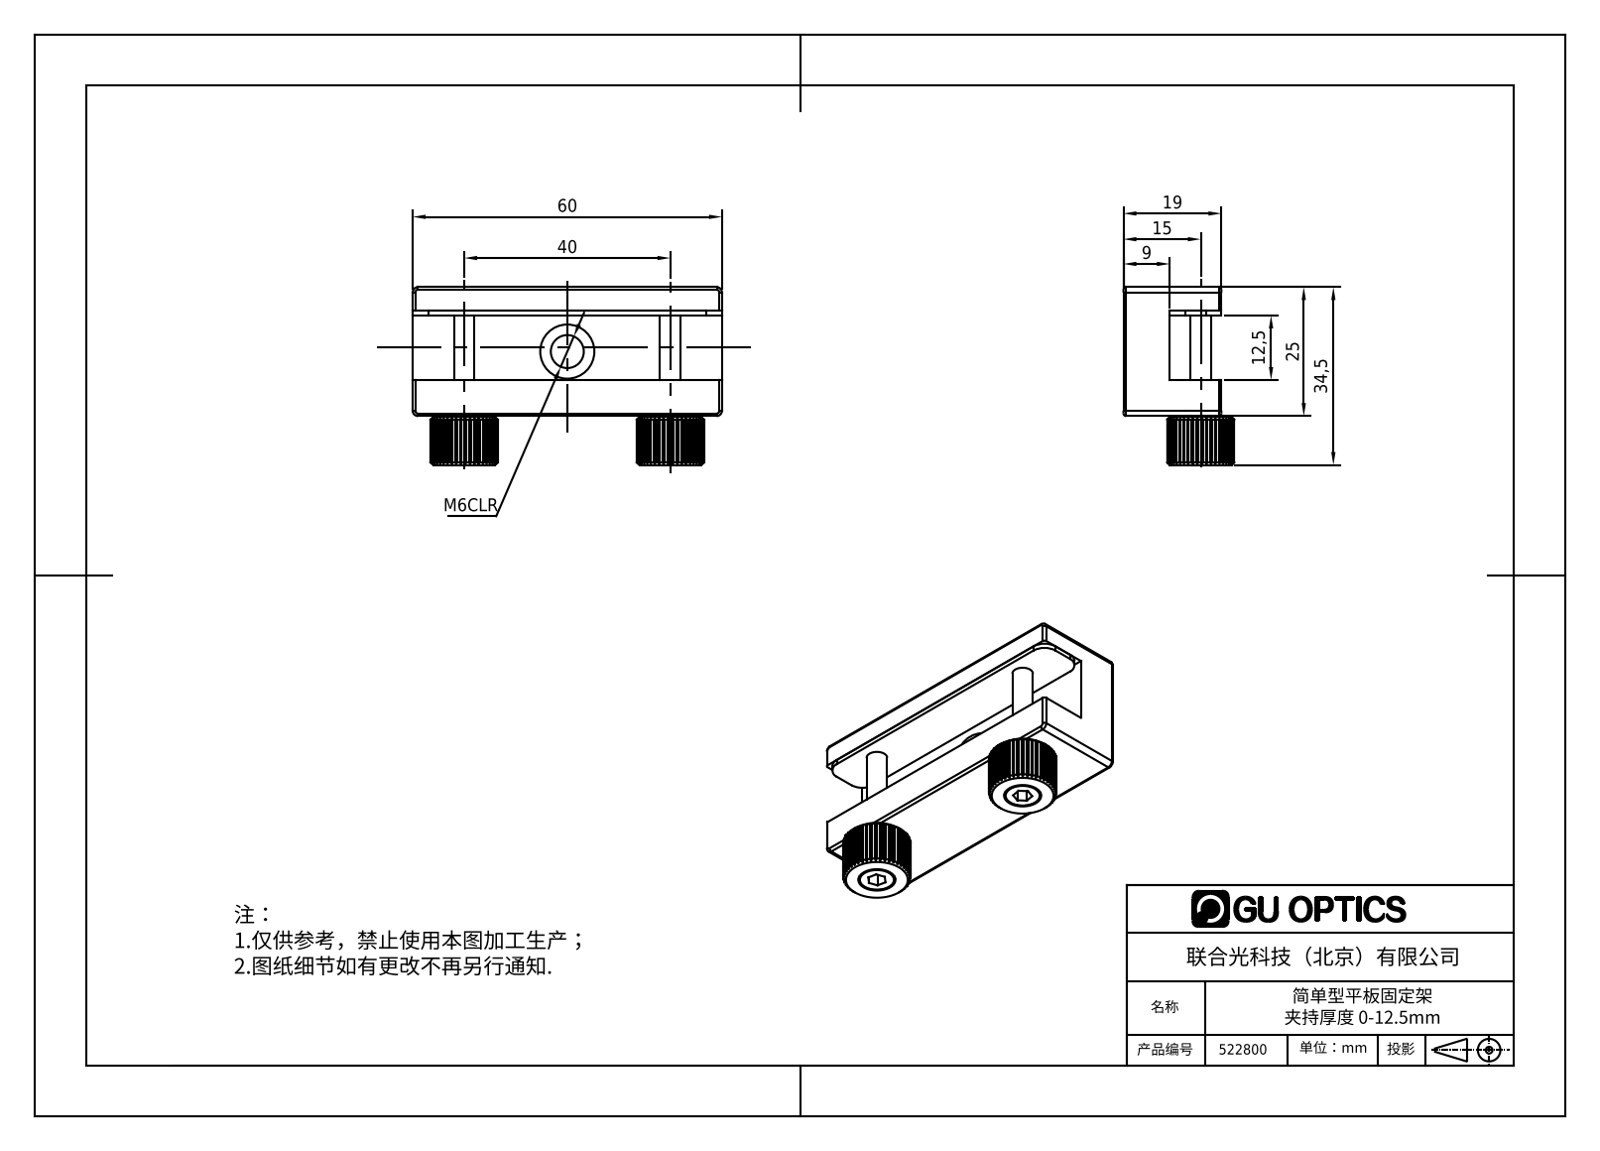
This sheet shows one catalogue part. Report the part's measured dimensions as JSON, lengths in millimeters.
{"part_name": "522800", "step_written_by": "SolidWorks 2020 (CONFIG_CONTROL_DESIGN)", "units": "millimeters", "bodies": {"solids": 0, "faces": 47, "planar": 18, "cylindrical": 14, "other": 15}, "overall_size": [62.6, 50, 23], "round_holes": [[12, 2], [14, 2]], "round_bosses_or_shafts": [[5, 3], [8, 2], [3.8, 2], [7.8, 1]], "partial_cylinders_radius": [[3.5, 2]], "face_to_face_distances": [7.8, 38.1, 22, 14.2, 30.3, 9.5, 20.8, 28.6, 50, 34], "hole_center_spacings": [30]}
